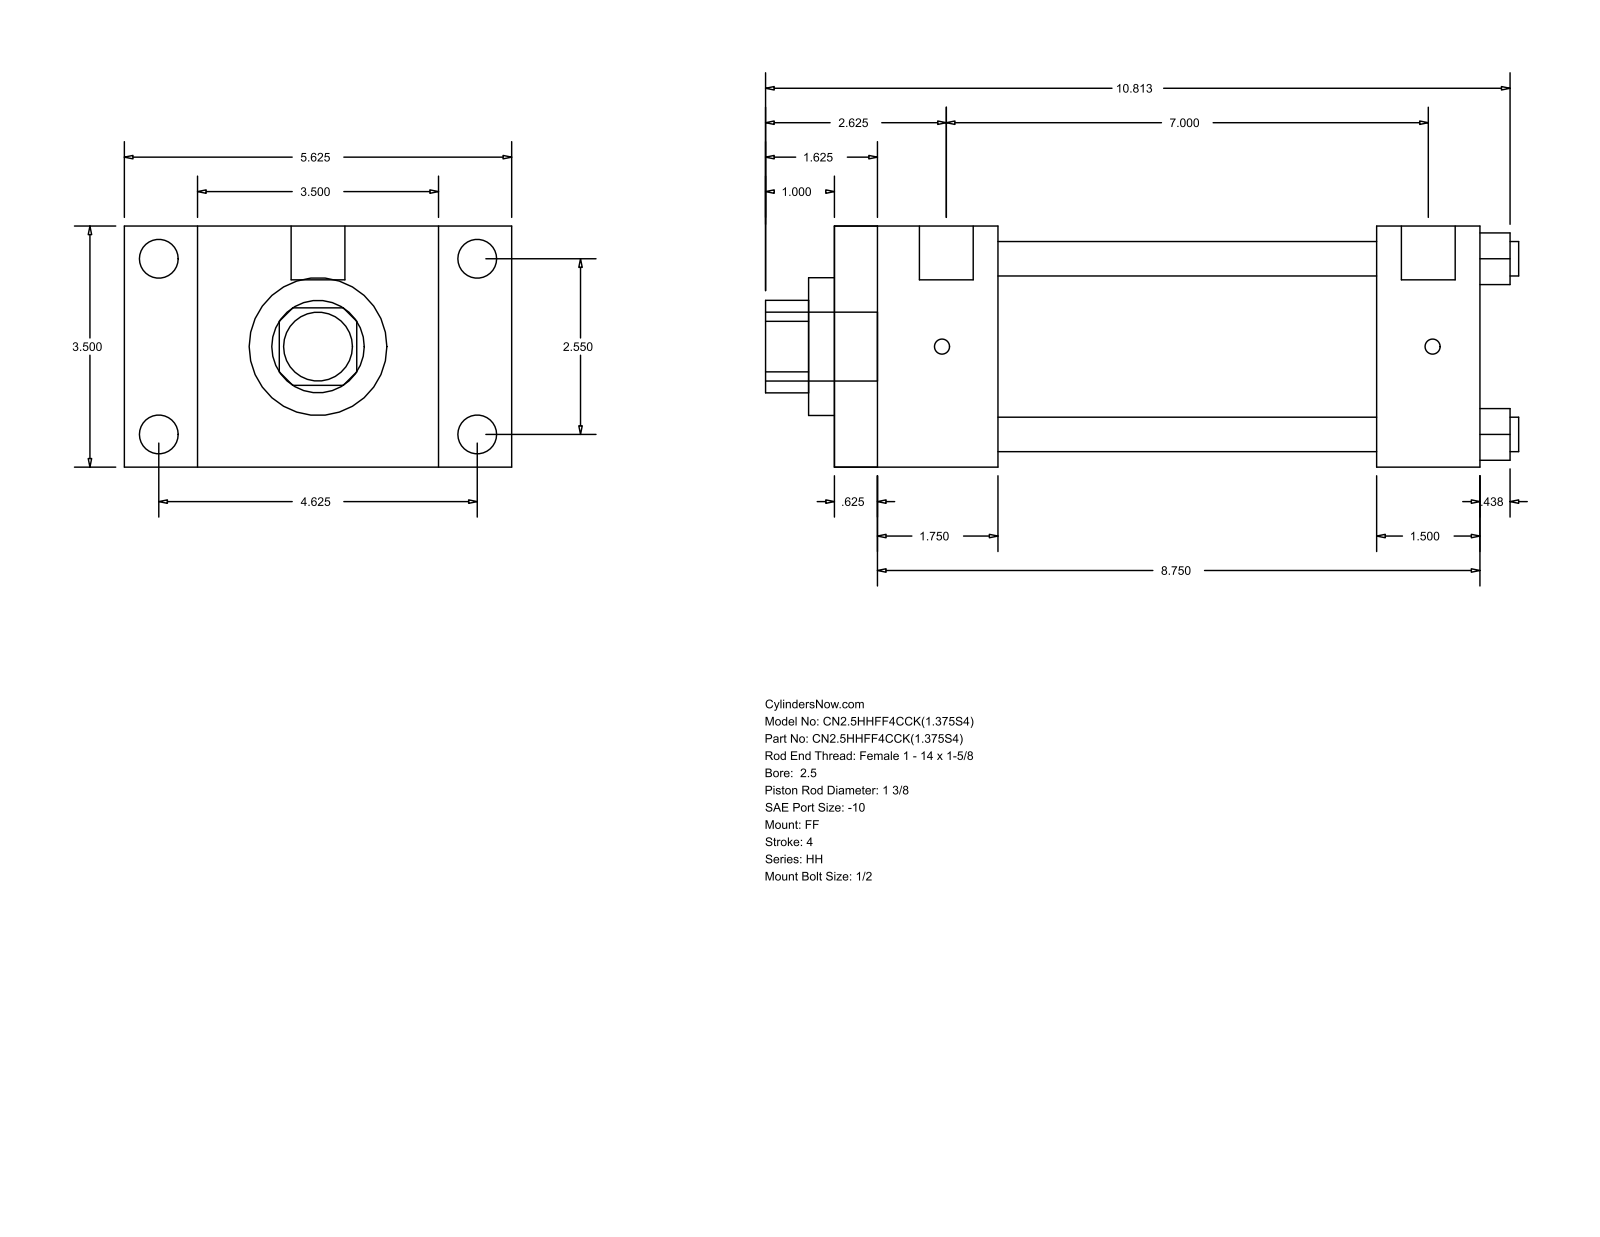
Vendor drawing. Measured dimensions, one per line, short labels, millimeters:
name: HH_FF__0250_1.375
written by: GSSL Pune (CONFIG_CONTROL_DESIGN)
unit: mm
bodies: 0 solids, 92 faces (64 planar, 28 cylindrical, 0 other)
size: 277.81 × 142.88 × 88.9
holes: 4× ⌀12.7, 1× ⌀34.92, 1× ⌀50.8, 1× ⌀73.03
bosses: 4× ⌀14.3, 4× ⌀5.56, 2× ⌀19.84, 1× ⌀25.4
rounds: 1× R17.06
face distances: 88.9, 238.12, 15.87, 222.25, 60.32, 44.45, 177.8, 200.03, 184.16, 139.71
hole spacings: 45.79, 64.76, 91.58
